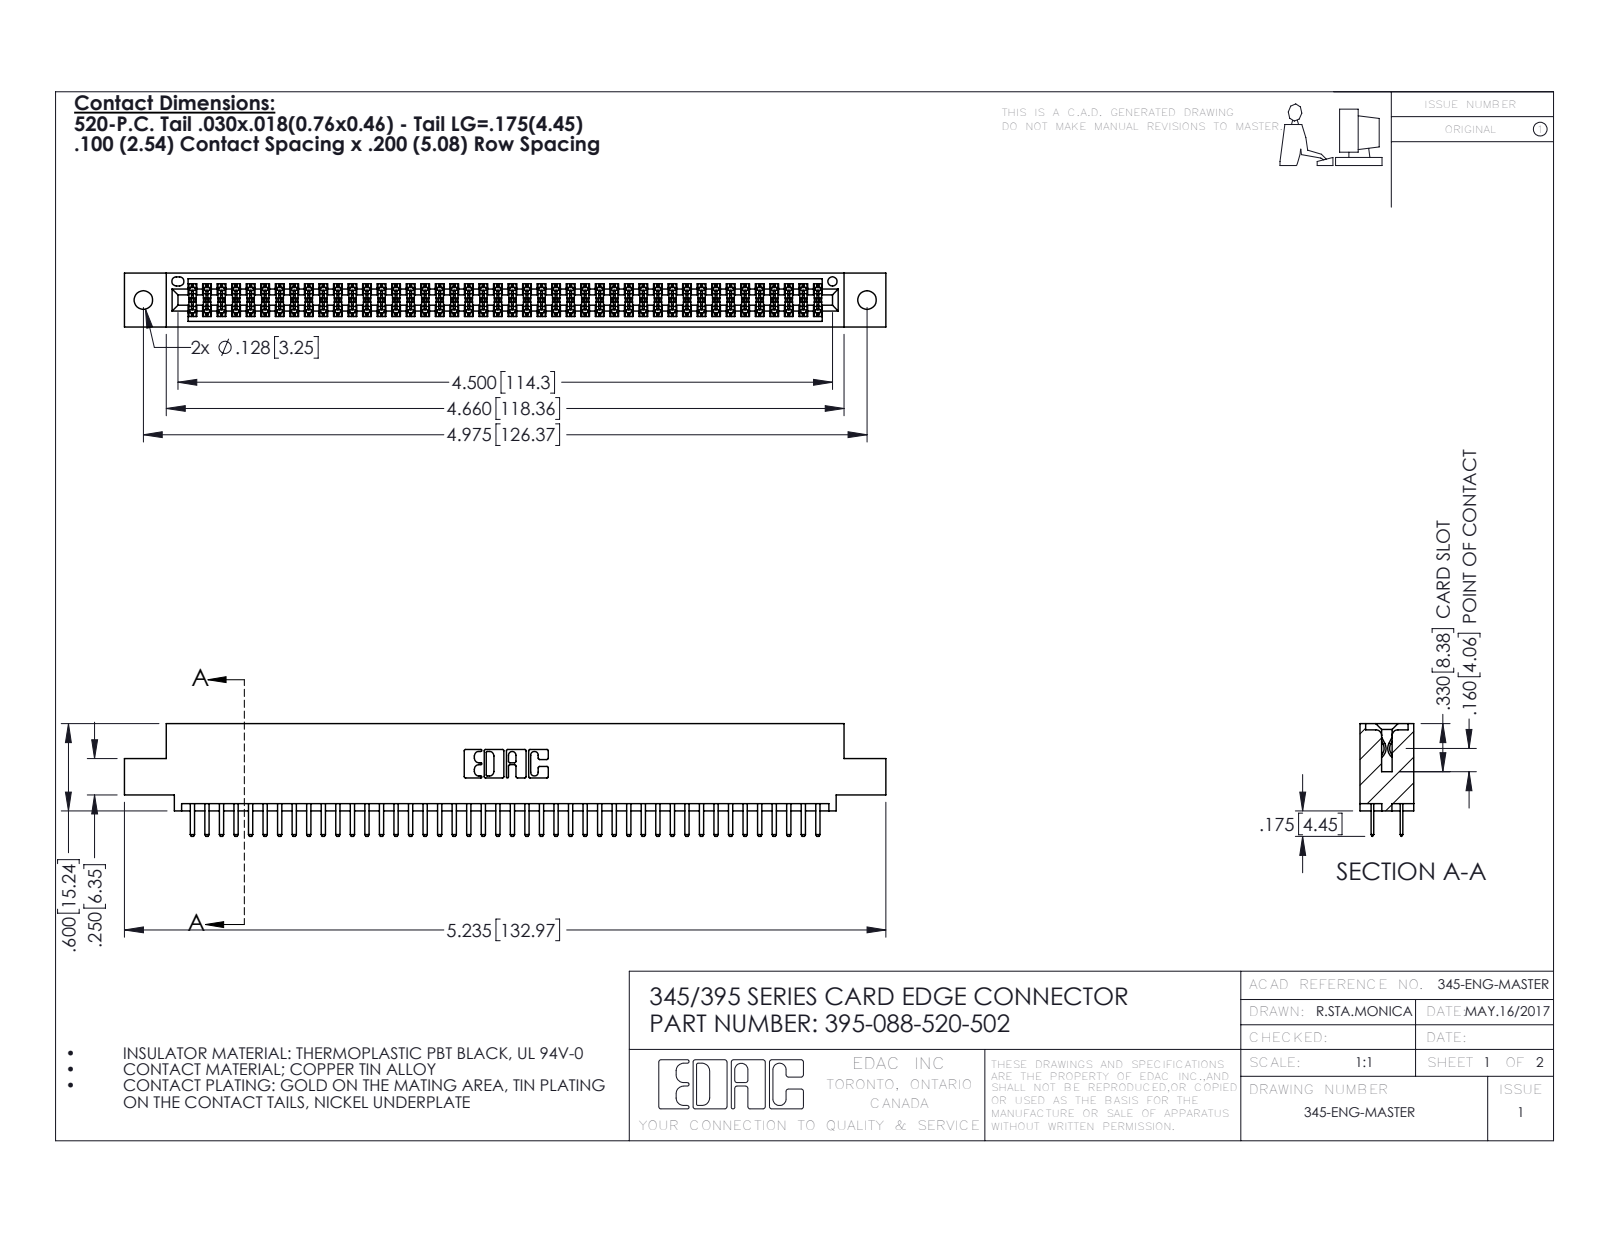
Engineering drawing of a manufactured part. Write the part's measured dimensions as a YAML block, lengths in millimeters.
part_name: "345 Part_0.110 Offset - 0.128 Dia; 345-292-001_345-293-120; 395-088-520-502"
step_written_by: "SolidWorks 2016 (CONFIG_CONTROL_DESIGN)"
units: millimeters
bodies: {solids: 89, faces: 4882, planar: 3164, cylindrical: 1718, other: 0}
overall_size: [133, 19.7, 9.4]
volume: 12800
surface_area: 18680
round_holes:
  - {diameter: 3.3, count: 2}
  - {diameter: 1.6, count: 1}
partial_cylinders:
  - {radius: 0.2, count: 132}
  - {radius: 0.3, count: 92}
  - {radius: 0.3, count: 22}
  - {radius: 0.2, count: 6}
  - {radius: 0.8, count: 6}
  - {radius: 0.7, count: 3}
  - {radius: 0.4, count: 2}
  - {radius: 0.5, count: 2}
face_to_face_distances: [7.6, 1.8, 5.1, 9.4, 2.5, 6.9, 0.6, 5.7, 0.6, 1.8]
hole_center_spacings: [6.9, 120.4, 126.4]
